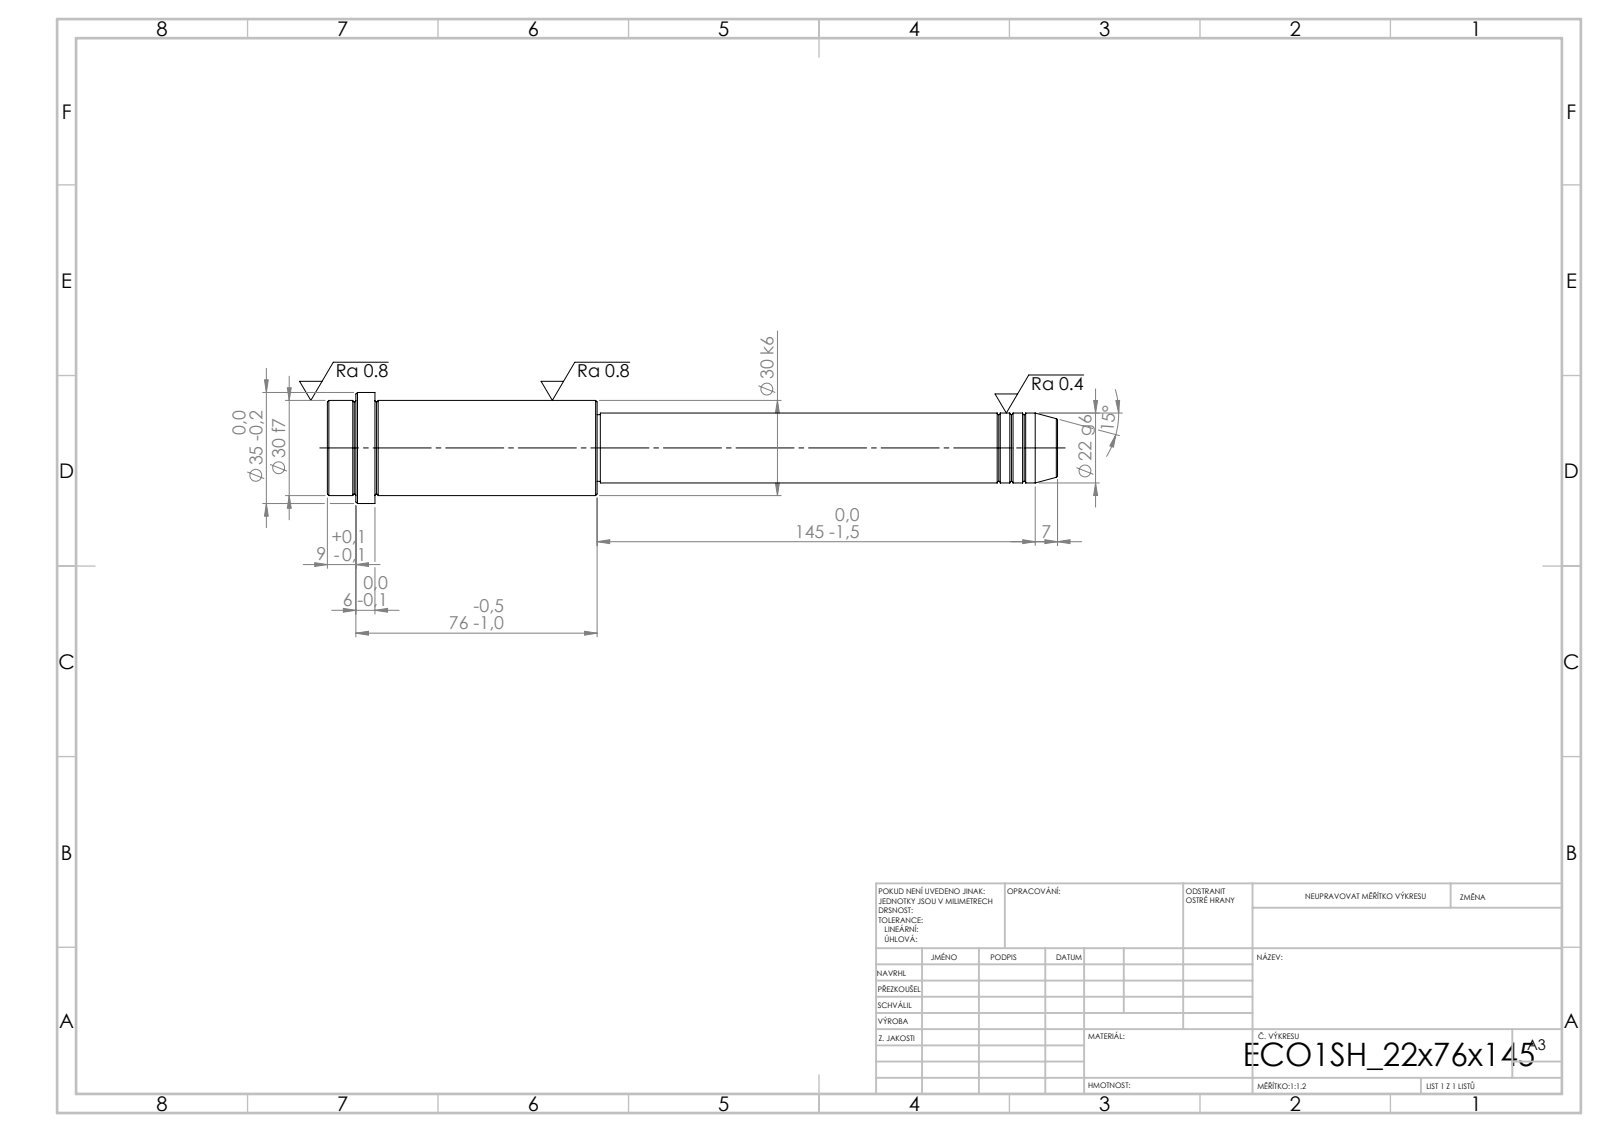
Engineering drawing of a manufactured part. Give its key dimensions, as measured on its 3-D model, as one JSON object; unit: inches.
{"step_written_by": "SolidWorks 2019 (CONFIG_CONTROL_DESIGN)", "units": "inches", "bodies": {"solids": 1, "faces": 52, "planar": 6, "cylindrical": 16, "other": 30}, "overall_size": [9.055, 1.378, 1.378], "volume_in3": 7.084, "surface_area_in2": 31.13, "round_bosses_or_shafts": [[1.378, 1], [1.181, 1], [0.866, 1], [0.827, 1]], "face_to_face_distances": [3.346, 2.756, 0.591, 5.709, 8.465, 9.055, 8.701, 2.992, 0.236, 0.354]}
